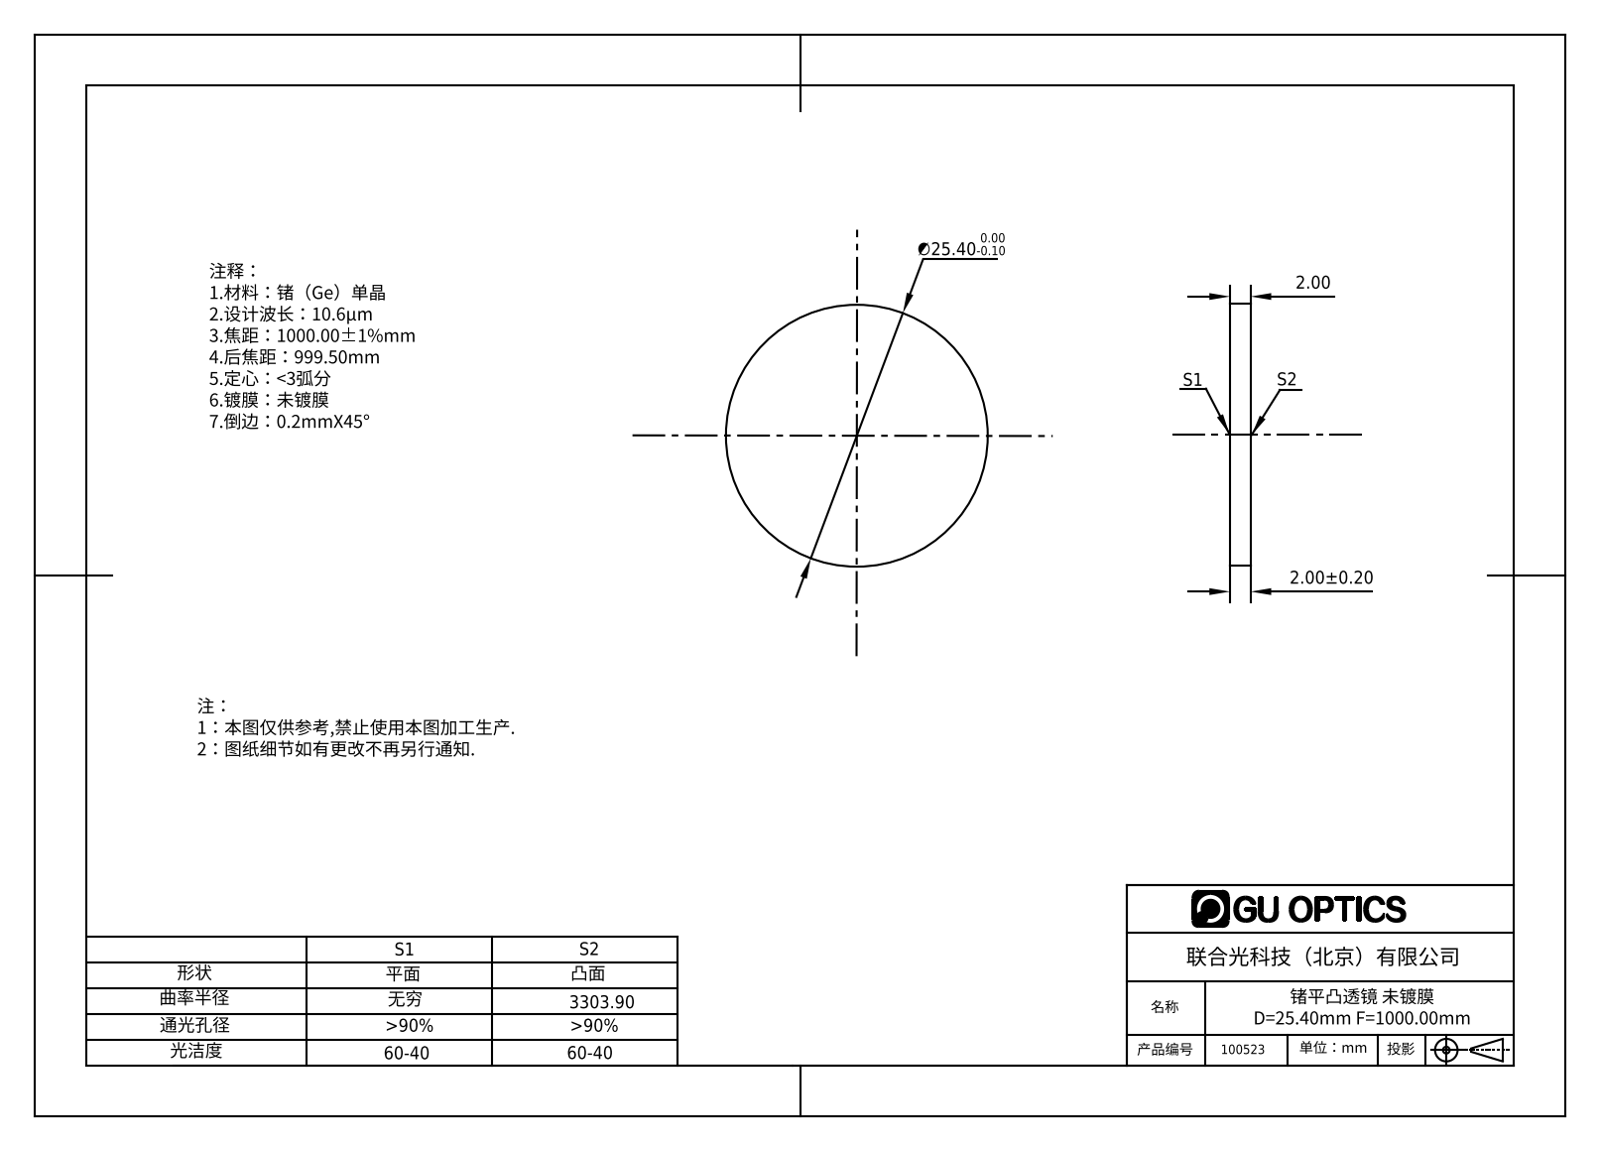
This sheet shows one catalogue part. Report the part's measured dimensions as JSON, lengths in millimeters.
{"part_name": "100522", "step_written_by": "SolidWorks 2016 (AUTOMOTIVE_DESIGN)", "units": "millimeters", "bodies": {"solids": 1, "faces": 4, "planar": 2, "cylindrical": 2, "other": 0}, "overall_size": [25.4, 25.4, 2], "volume_mm3": 1013, "surface_area_mm2": 1173, "round_bosses_or_shafts": [[25.4, 1]], "face_to_face_distances": [2]}
